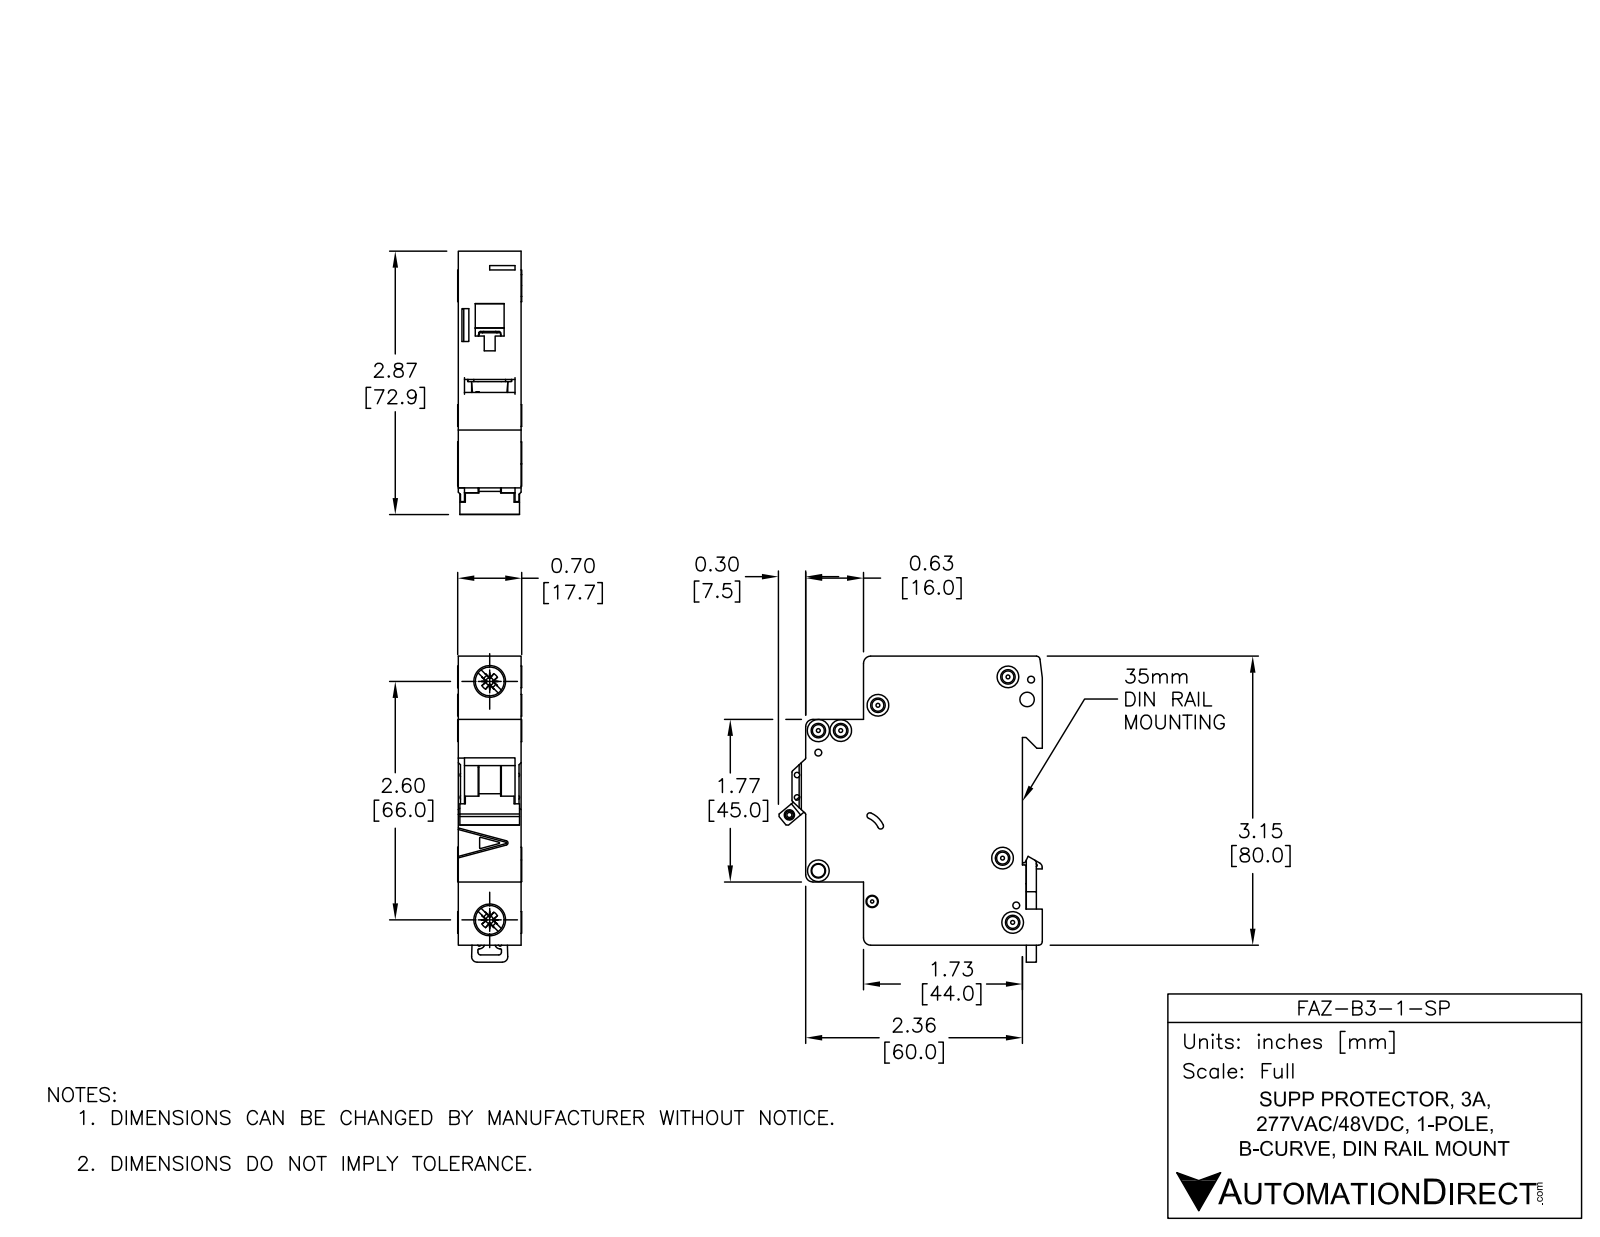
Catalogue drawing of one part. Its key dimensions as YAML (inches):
part_name: "FAZ-B3-1-SP"
step_written_by: "SolidWorks 2014 (AUTOMOTIVE_DESIGN)"
units: inches
bodies: {solids: 5, faces: 558, planar: 235, cylindrical: 202, other: 121}
overall_size: [3.338, 2.876, 0.697]
volume: 4.573
surface_area: 30.29
round_holes:
  - {diameter: 0.142, count: 6}
  - {diameter: 0.075, count: 3}
  - {diameter: 0.043, count: 2}
  - {diameter: 0.059, count: 2}
  - {diameter: 0.157, count: 2}
  - {diameter: 0.281, count: 2}
  - {diameter: 0.085, count: 1}
  - {diameter: 0.087, count: 1}
  - {diameter: 0.1, count: 1}
  - {diameter: 0.13, count: 1}
  - {diameter: 0.134, count: 1}
round_bosses_or_shafts:
  - {diameter: 0.236, count: 4}
  - {diameter: 0.323, count: 2}
  - {diameter: 0.098, count: 1}
partial_cylinders:
  - {radius: 0.01, count: 30}
  - {radius: 0.02, count: 13}
  - {radius: 0.079, count: 8}
  - {radius: 0.008, count: 5}
  - {radius: 0.039, count: 4}
  - {radius: 0.031, count: 2}
  - {radius: 0.118, count: 2}
  - {radius: 0.059, count: 1}
face_to_face_distances: [0.689, 3.129, 0.217, 1.949, 1.732, 2.579, 2.362, 0.63, 0.069, 0.62]
hole_center_spacings: [0.244, 0.537, 0.189, 0.204, 0.221, 0.24, 0.254, 0.322]
